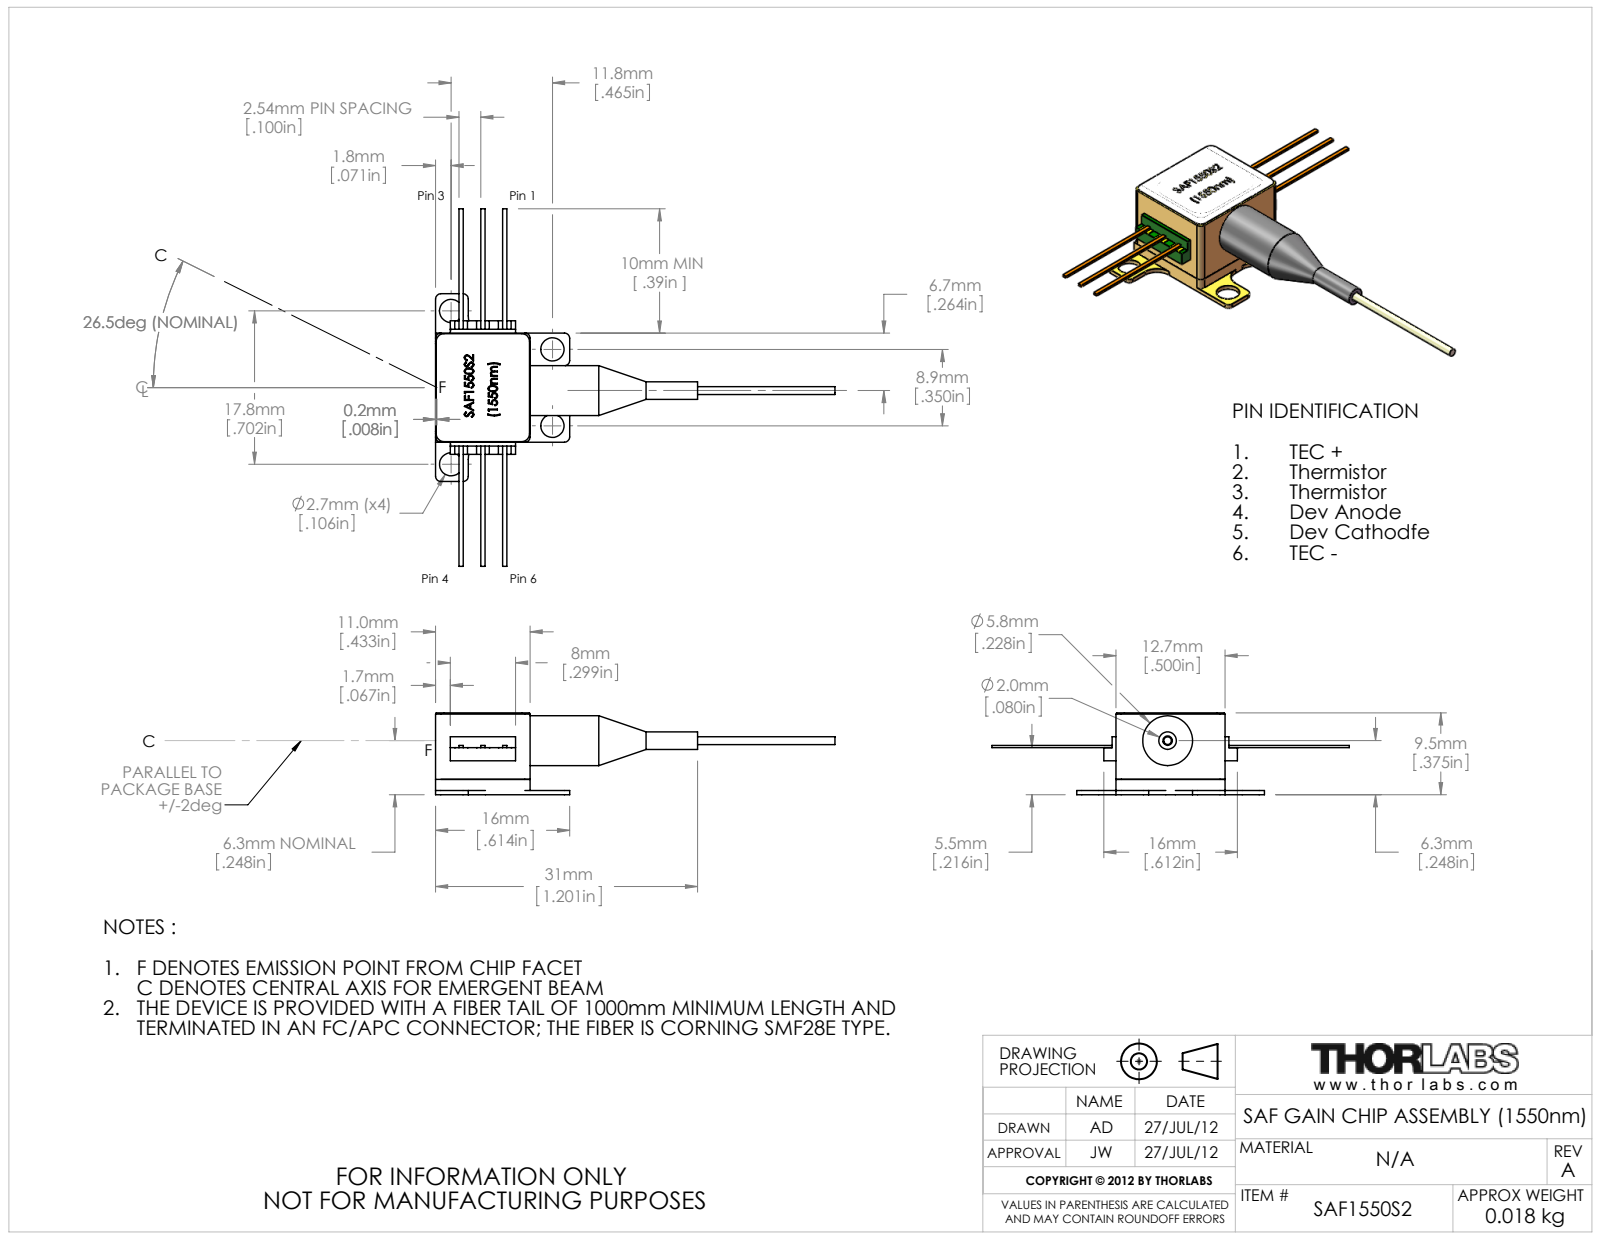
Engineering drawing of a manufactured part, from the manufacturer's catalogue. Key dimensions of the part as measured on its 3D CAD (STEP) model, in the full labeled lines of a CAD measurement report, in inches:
Part name (STEP PRODUCT): 24726-E0W
STEP written by: SolidWorks 2011 (AUTOMOTIVE_DESIGN)
Units: inches
Bodies: 15 solids, 491 faces (306 planar, 70 cylindrical, 115 other)
Overall size (bounding box): 1.831 × 1.638 × 0.375
Volume: 0.057 in³ · Surface area: 3.759 in²
Round holes (diameter × count): ⌀0.106 ×4, ⌀0.043 ×1, ⌀0.082 ×1, ⌀0.125 ×1, ⌀0.161 ×1
Round bosses / shafts (diameter × count): ⌀0.228 ×1, ⌀0.136 ×1, ⌀0.08 ×1, ⌀0.035 ×1
Partial cylindrical surfaces — rounded edges, fillets, slot ends (radius × count): R0.024 ×12, R0.039 ×10, R0.005 ×4, R0.012 ×4, R0.035 ×4, R0.073 ×4, R0.079 ×4
Main face-to-face distances: 0.039, 0.063, 0.375, 0.312, 0.299, 0.37, 0.307, 0.071, 0.057, 0.461
Hole centre spacings: 0.497, 0.702, 0.35, 0.702
